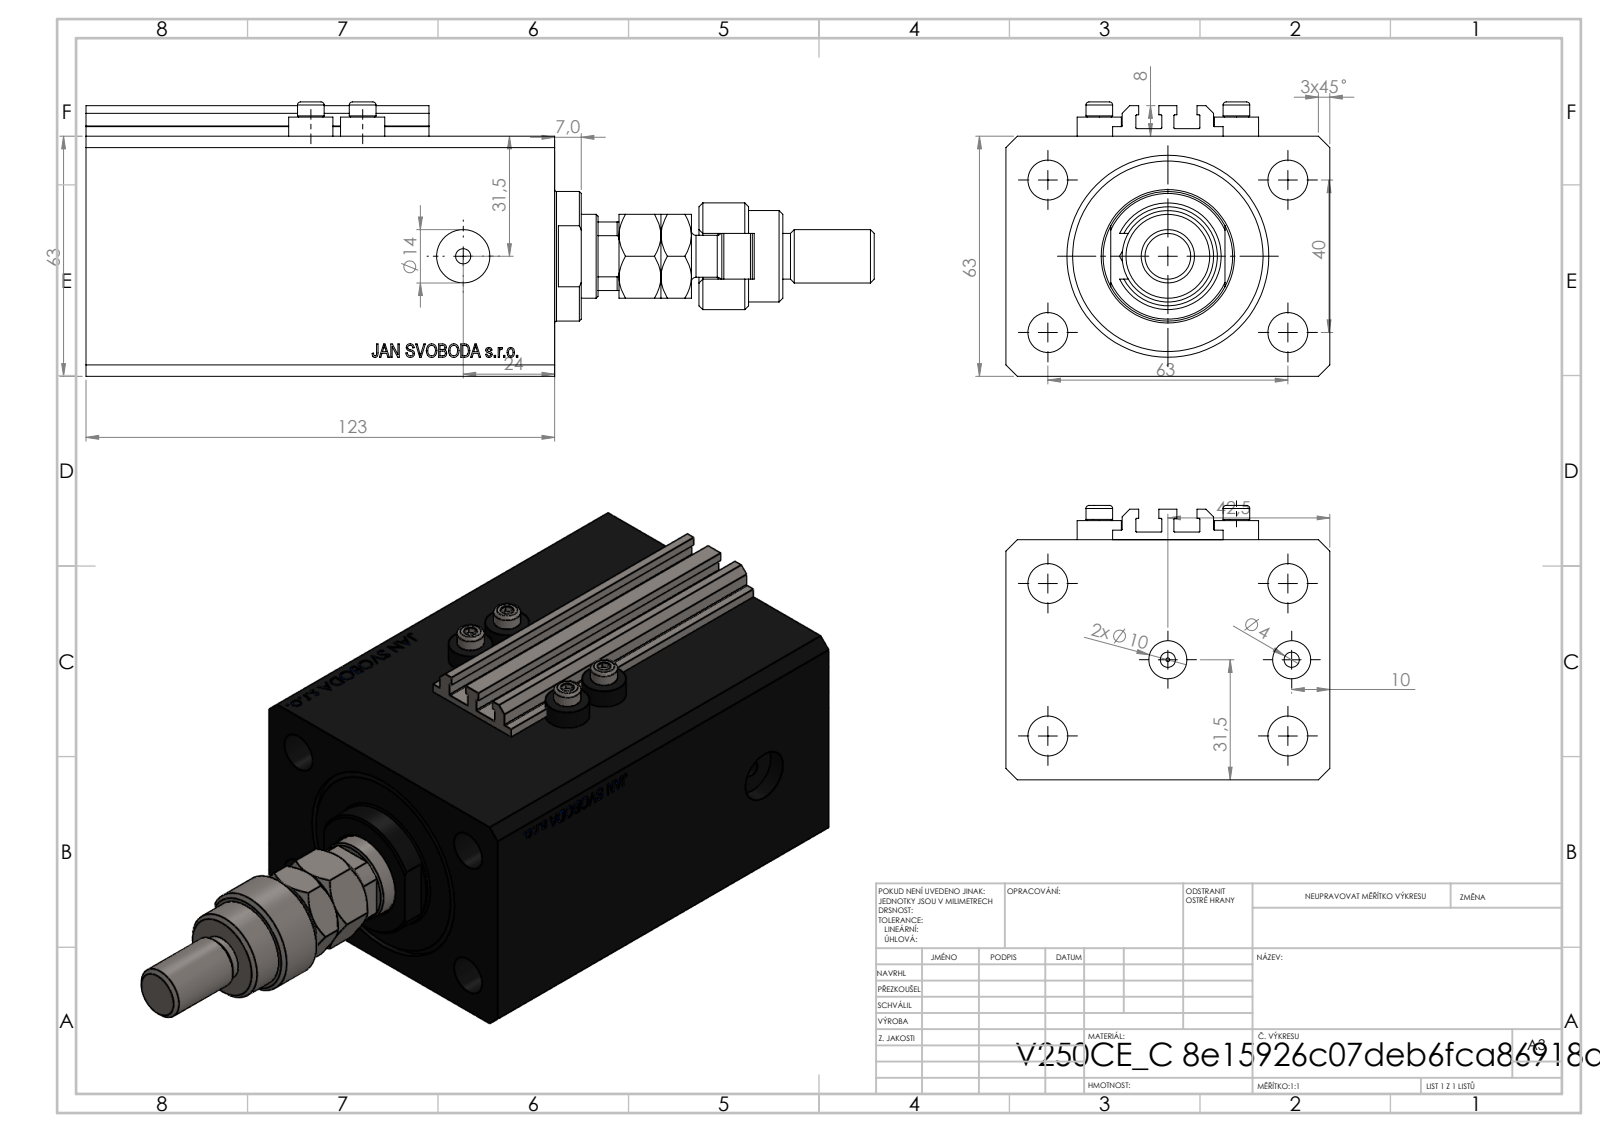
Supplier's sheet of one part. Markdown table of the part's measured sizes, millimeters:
| quantity | value |
| --- | --- |
| part name | MFA; V250CE_C_Body; ALLEN BOLT V250CE; FEMALE_PART_FOR_DFA (+2 more) |
| STEP written by | SolidWorks 2019 (CONFIG_CONTROL_DESIGN) |
| units | millimeters |
| bodies | 10 solids, 1123 faces (532 planar, 101 cylindrical, 490 other) |
| overall size | 206.9 × 85 × 72 |
| volume | 608 816 mm³ |
| surface area | 124 278 mm² |
| round holes (diameter × count) | 4 × 8, 10.5 × 4, 10 × 2, 14 × 2, 1.25 × 1, 12.5 × 1, 22 × 1, 40 × 1, 53 × 1 |
| round bosses / shafts (diameter × count) | 11.6 × 4, 7 × 4, 34 × 1, 28 × 1, 24 × 1, 18 × 1, 14 × 1, 12 × 1 |
| partial cylindrical surfaces (radius × count) | 0.2 × 10, 9.75 × 1, 10.5 × 1 |
| main face-to-face distances | 63, 85, 123, 95.9, 27.1, 11.4, 84.5, 111.6, 2, 8 |
| hole center spacings | 37.31, 13.6, 20.02, 36, 38.48, 40, 63, 67.05 |
